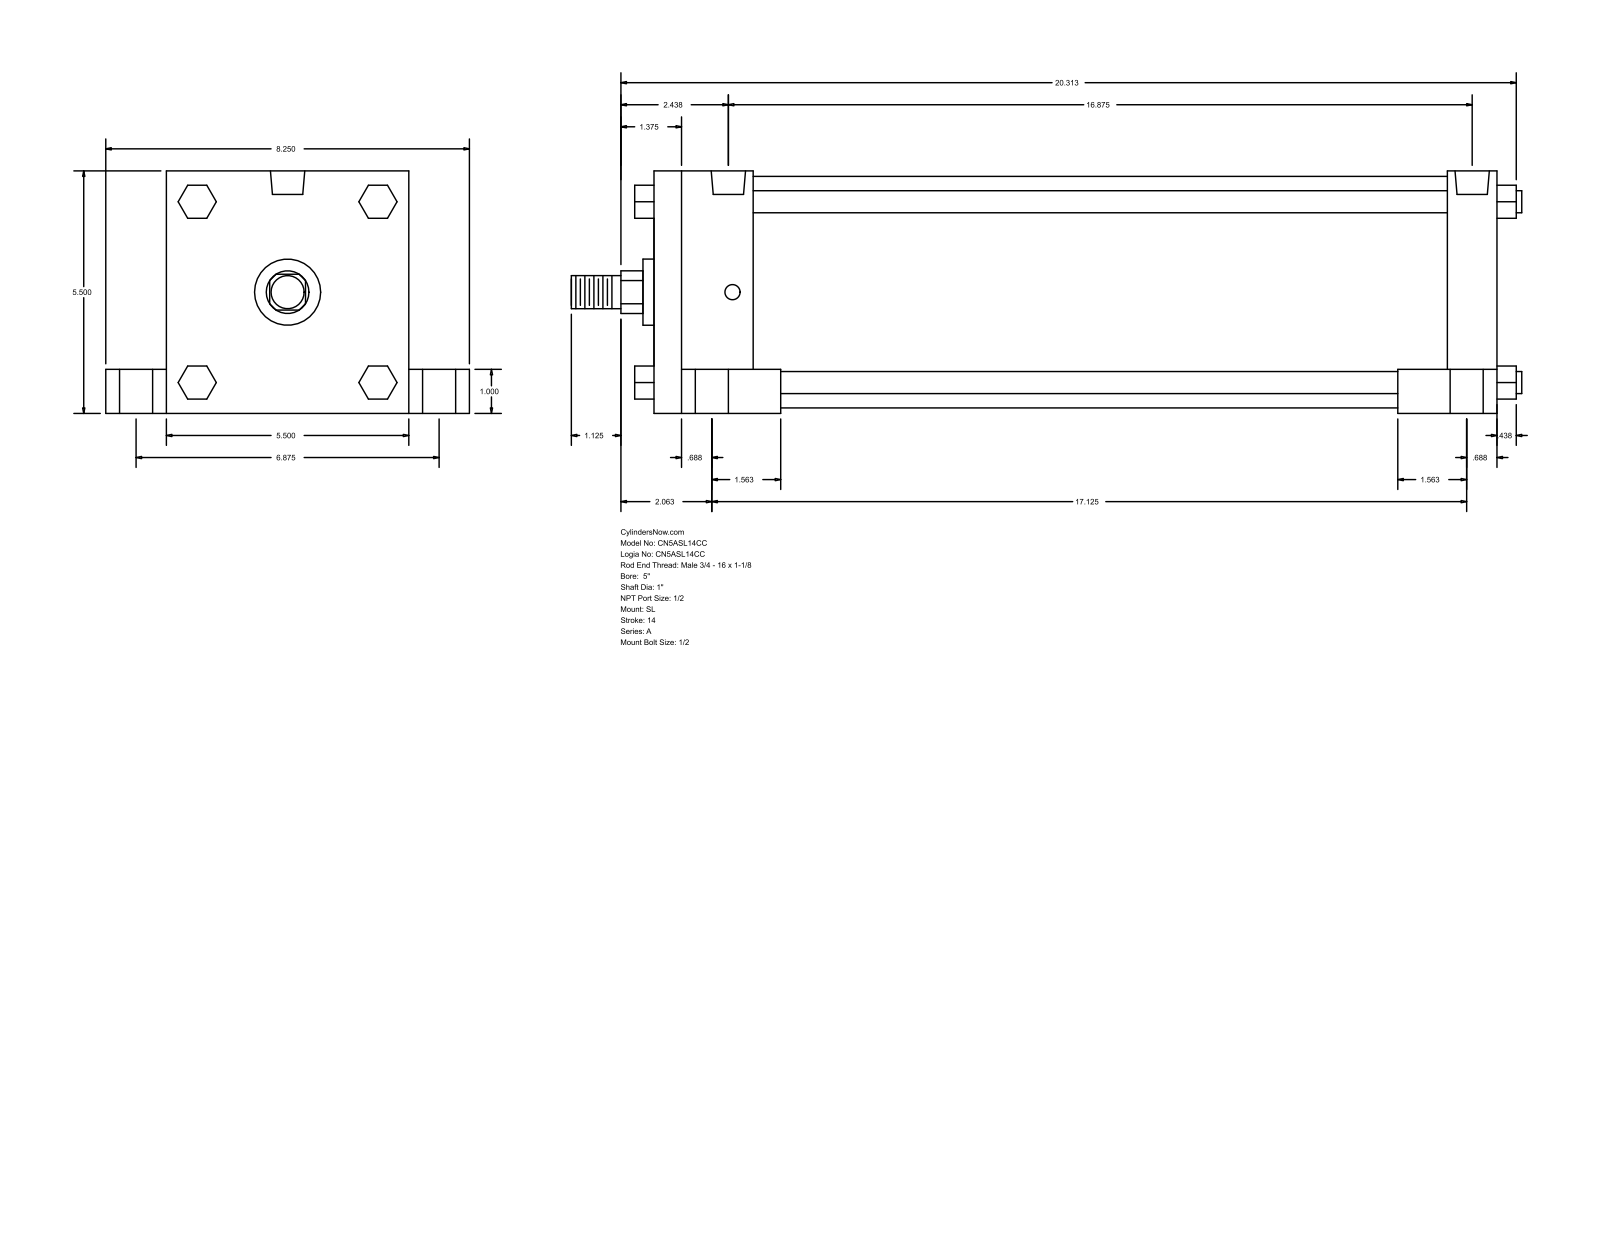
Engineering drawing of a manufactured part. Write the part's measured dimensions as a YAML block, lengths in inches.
part_name: "A_SL__0500_1"
step_written_by: "GSSL Pune (CONFIG_CONTROL_DESIGN)"
units: inches
bodies: {solids: 0, faces: 150, planar: 114, cylindrical: 36, other: 0}
overall_size: [21.563, 8.25, 5.5]
round_holes:
  - {diameter: 0.344, count: 4}
  - {diameter: 0.75, count: 4}
  - {diameter: 1, count: 4}
  - {diameter: 0.778, count: 2}
round_bosses_or_shafts:
  - {diameter: 0.5, count: 4}
  - {diameter: 5.25, count: 1}
  - {diameter: 1.5, count: 1}
  - {diameter: 1, count: 1}
  - {diameter: 0.75, count: 1}
partial_cylinders:
  - {radius: 0.484, count: 1}
face_to_face_distances: [5.5, 19.125, 1.125, 1, 4.5, 1.375, 6.875, 2.25, 18, 15.75]
hole_center_spacings: [0.094, 3.437, 3.44, 3.458, 3.469, 6.875, 16.687, 16.781]
